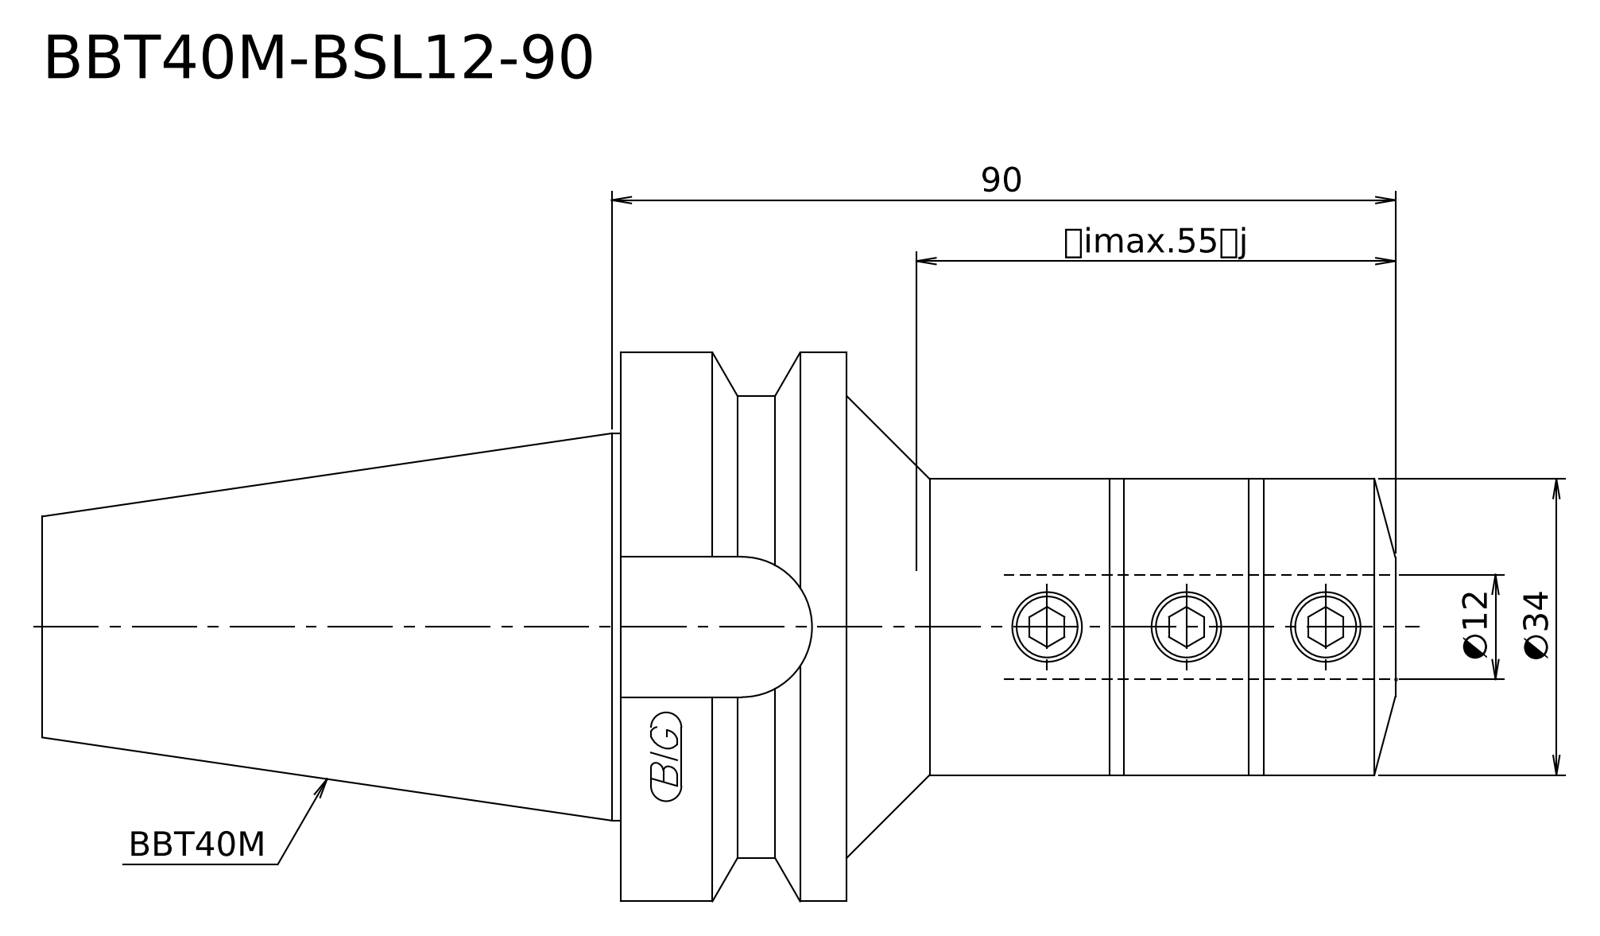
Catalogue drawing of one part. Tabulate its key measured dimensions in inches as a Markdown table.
| quantity | value |
| --- | --- |
| STEP written by | Kubotek KeyCreator V8.5.1 (14335) (CONFIG_CONTROL_DESIGN) |
| units | inches |
| bodies | 1 solid, 14 faces (4 planar, 5 cylindrical, 5 other) |
| overall size | 6.118 × 2.48 × 2.48 |
| volume | 12.34 in³ |
| surface area | 38.09 in² |
| round bosses / shafts (diameter × count) | 2.48 × 1, 2.087 × 1, 1.75 × 1, 1.339 × 1 |
| main face-to-face distances | 1.024, 3.638, 2.614, 2.48, 3.504, 6.118 |
